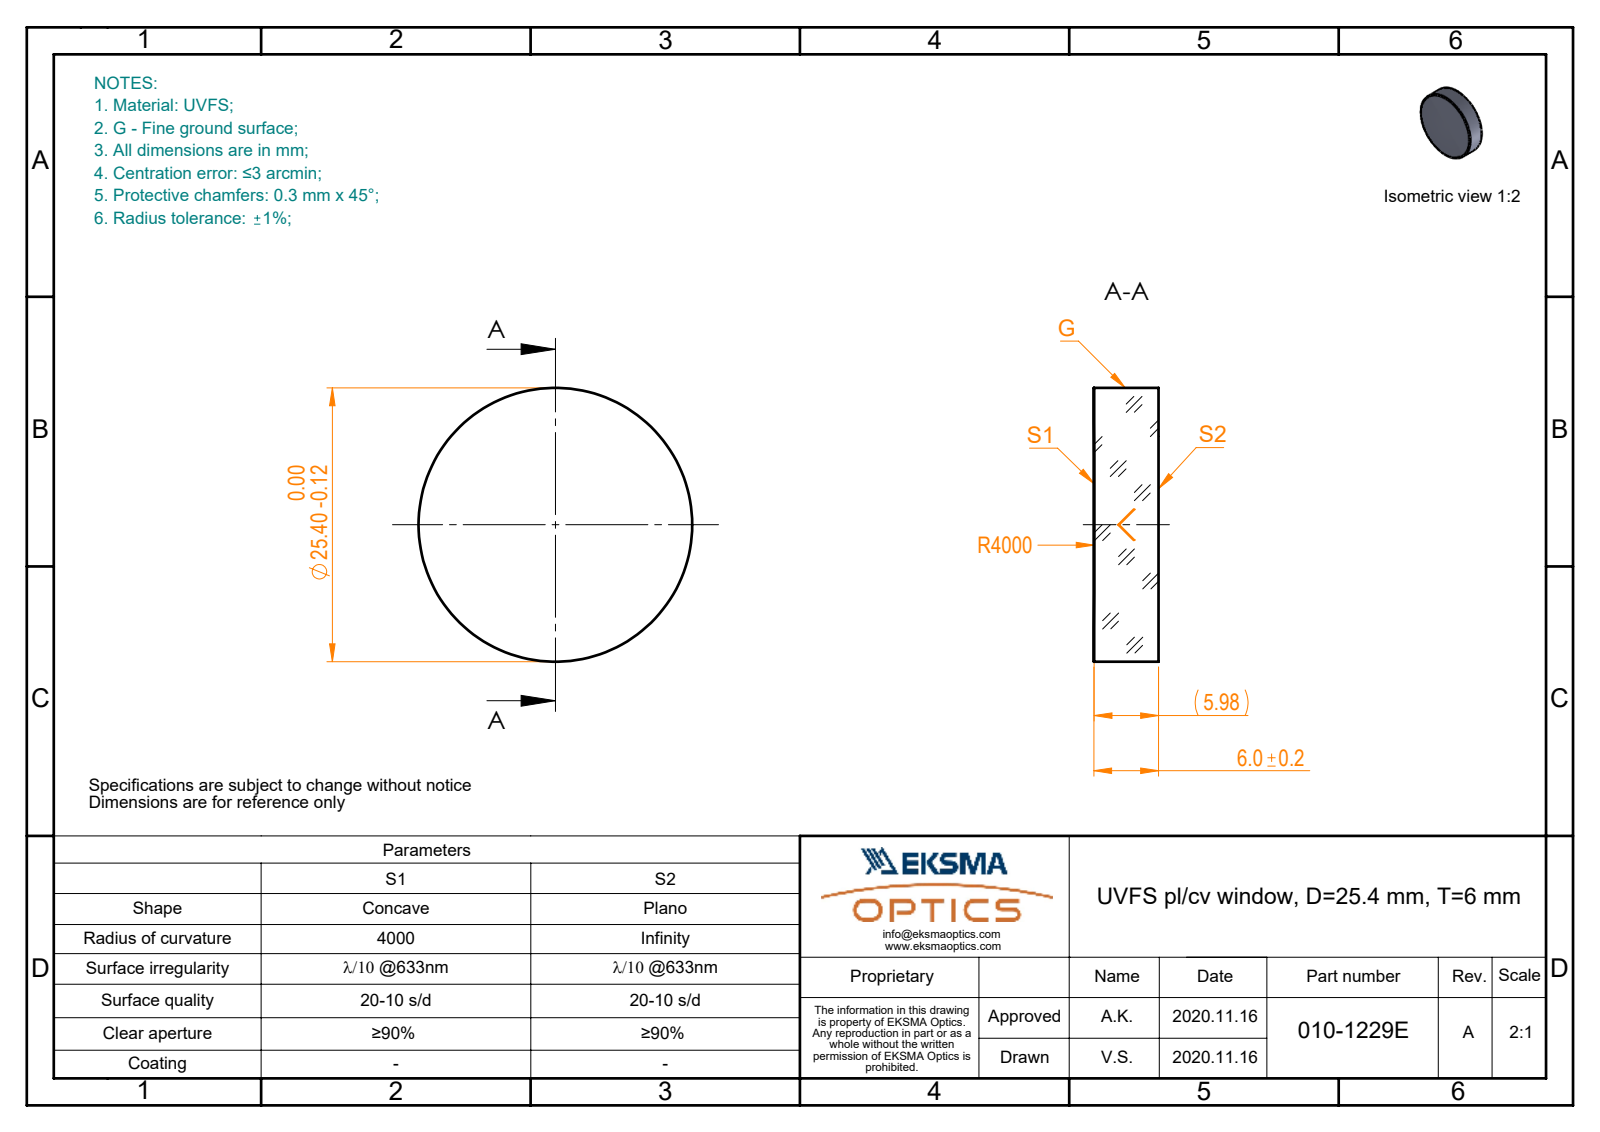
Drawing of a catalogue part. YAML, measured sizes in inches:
part_name: "010-1229E_UVFS_PCV_window"
step_written_by: "SolidWorks 2019 (CONFIG_CONTROL_DESIGN)"
units: inches
bodies: {solids: 1, faces: 5, planar: 1, cylindrical: 2, other: 2}
overall_size: [1, 1, 0.236]
volume: 0.185
surface_area: 2.313
round_bosses_or_shafts:
  - {diameter: 1, count: 1}
